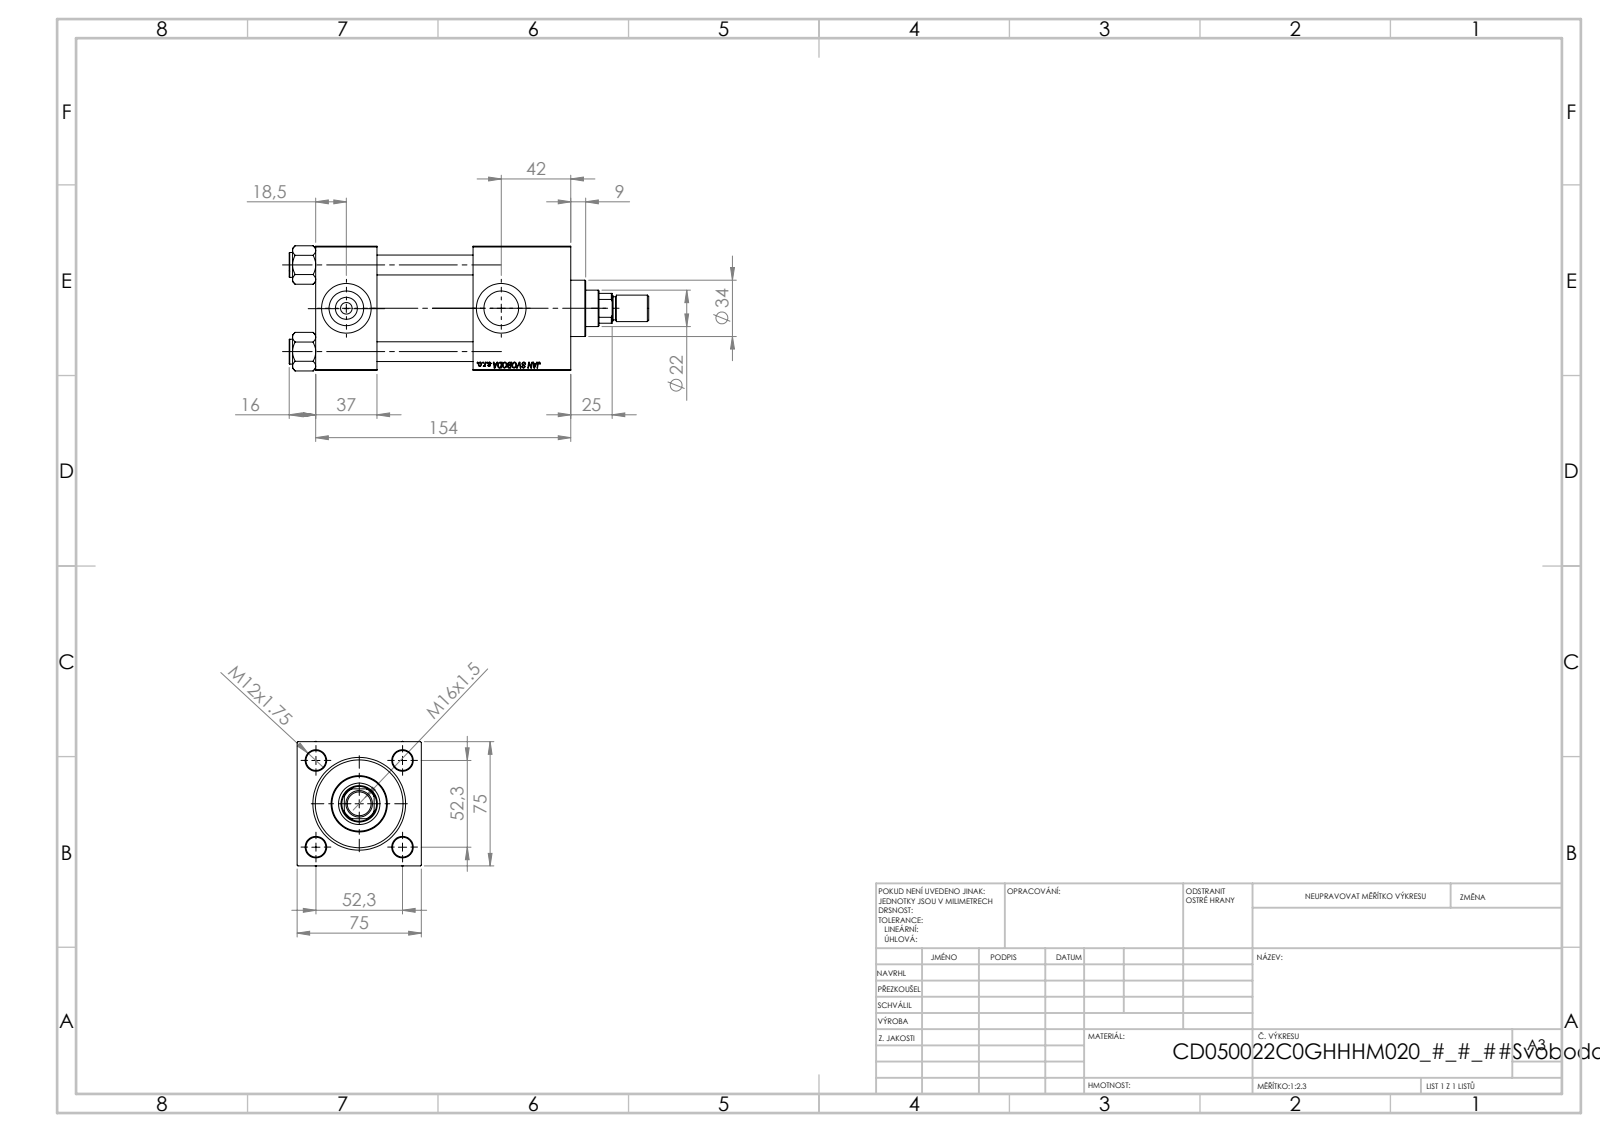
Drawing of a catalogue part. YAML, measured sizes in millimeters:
part_name: "NUT_M5_V215CD_C; V215CD_C_TYCINKA; ROD_END_AH; V215CD_Body_C (+2 more)"
step_written_by: "SolidWorks 2019 (CONFIG_CONTROL_DESIGN)"
units: millimeters
bodies: {solids: 12, faces: 1162, planar: 530, cylindrical: 90, other: 542}
overall_size: [217, 75.54, 75]
volume: 661273
surface_area: 148826
round_holes:
  - {diameter: 12, count: 4}
  - {diameter: 7, count: 2}
  - {diameter: 20.96, count: 2}
  - {diameter: 30, count: 2}
  - {diameter: 10.5, count: 1}
  - {diameter: 22, count: 1}
  - {diameter: 25, count: 1}
  - {diameter: 41, count: 1}
  - {diameter: 50, count: 1}
  - {diameter: 53, count: 1}
round_bosses_or_shafts:
  - {diameter: 15, count: 4}
  - {diameter: 56, count: 1}
  - {diameter: 34, count: 1}
  - {diameter: 16, count: 1}
  - {diameter: 14, count: 1}
partial_cylinders:
  - {radius: 10.5, count: 1}
face_to_face_distances: [75, 37, 154, 117, 95, 58, 59, 125.3, 88.3, 30.3]
hole_center_spacings: [36.98, 52.3, 73.96, 93.5]
